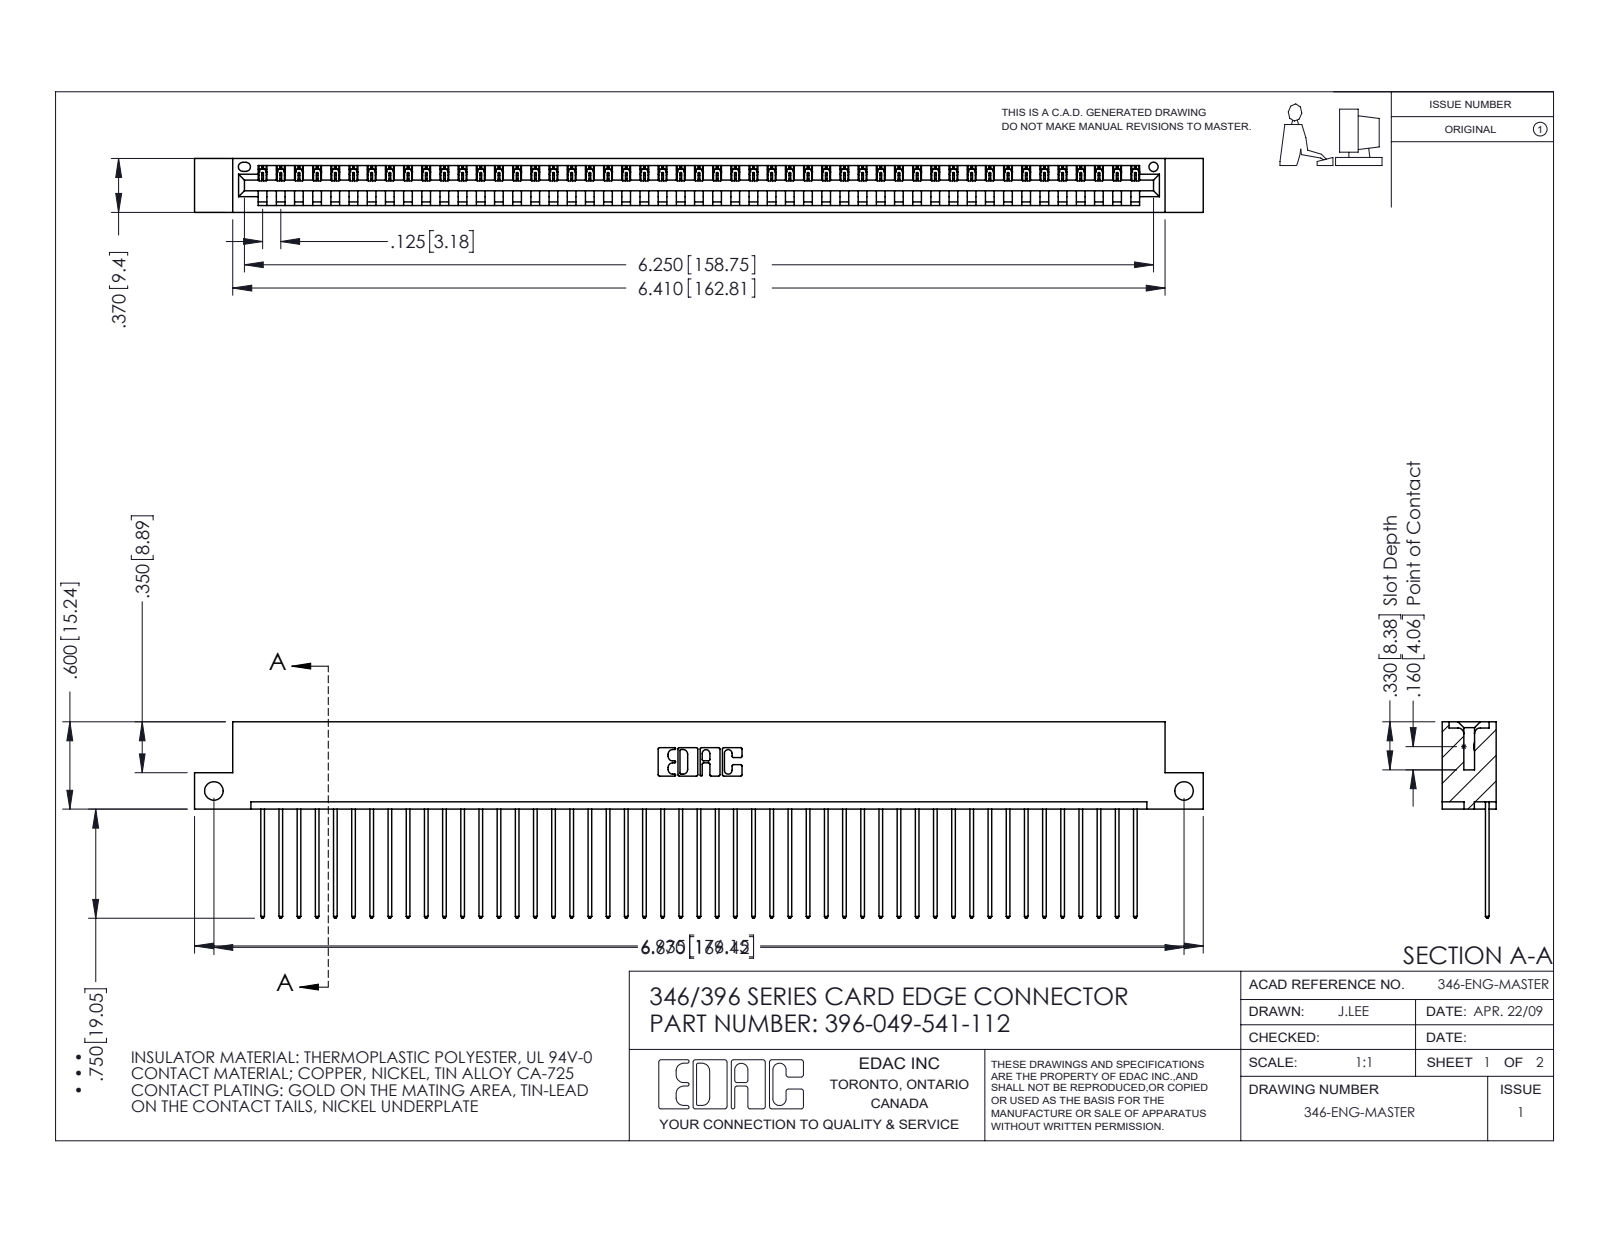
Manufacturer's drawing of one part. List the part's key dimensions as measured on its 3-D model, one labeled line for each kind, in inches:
Part name (STEP PRODUCT): 346 Part_Flush Mounting Lugs - Side Mount; 345-292-001_345-293-141; 396-049-541-112
STEP written by: SolidWorks 2016 (CONFIG_CONTROL_DESIGN)
Units: inches
Bodies: 50 solids, 2964 faces (2036 planar, 928 cylindrical, 0 other)
Overall size (bounding box): 6.935 × 1.35 × 0.37
Volume: 1.036 in³ · Surface area: 34.29 in²
Round holes (diameter × count): ⌀0.128 ×2, ⌀0.064 ×1
Partial cylindrical surfaces — rounded edges, fillets, slot ends (radius × count): R0.006 ×98, R0.01 ×98, R0.01 ×22, R0.007 ×6, R0.031 ×6, R0.026 ×3, R0.031 ×2, R0.04 ×2
Main face-to-face distances: 0.048, 0.322, 0.37, 0.25, 0.072, 0.298, 0.025, 0.148, 0.222, 0.1
Hole centre spacings: 6.67
